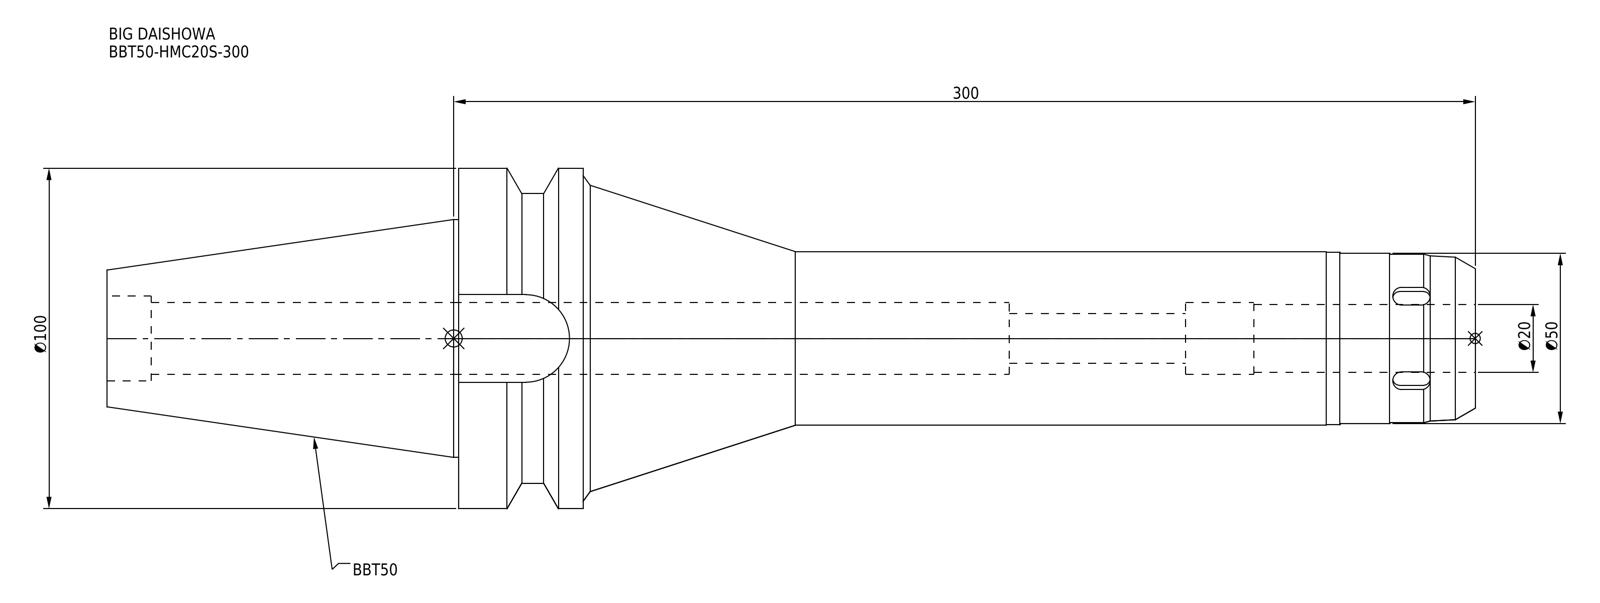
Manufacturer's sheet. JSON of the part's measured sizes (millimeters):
{"part_name": "BBT50-HMC20S-300", "step_written_by": "CREO PARAMETRIC BY PTC INC, 2016380 (AUTOMOTIVE_DESIGN)", "units": "millimeters", "bodies": {"solids": 1, "faces": 97, "planar": 33, "cylindrical": 40, "other": 24}, "overall_size": [401.8, 100, 100], "volume_mm3": 1023000, "surface_area_mm2": 112085, "round_holes": [[14.5, 1], [20, 1], [21, 1], [21.2, 1], [25, 1]], "round_bosses_or_shafts": [[100, 1], [85, 1], [69.85, 1], [51, 1], [50.7, 1], [50, 1], [49.5, 1]], "partial_cylinders_radius": [[3, 6], [12.85, 1]], "face_to_face_distances": [298.5, 401.8, 103.3, 70.8, 262, 36.5, 139.8, 25.7, 136.8, 125.2]}
